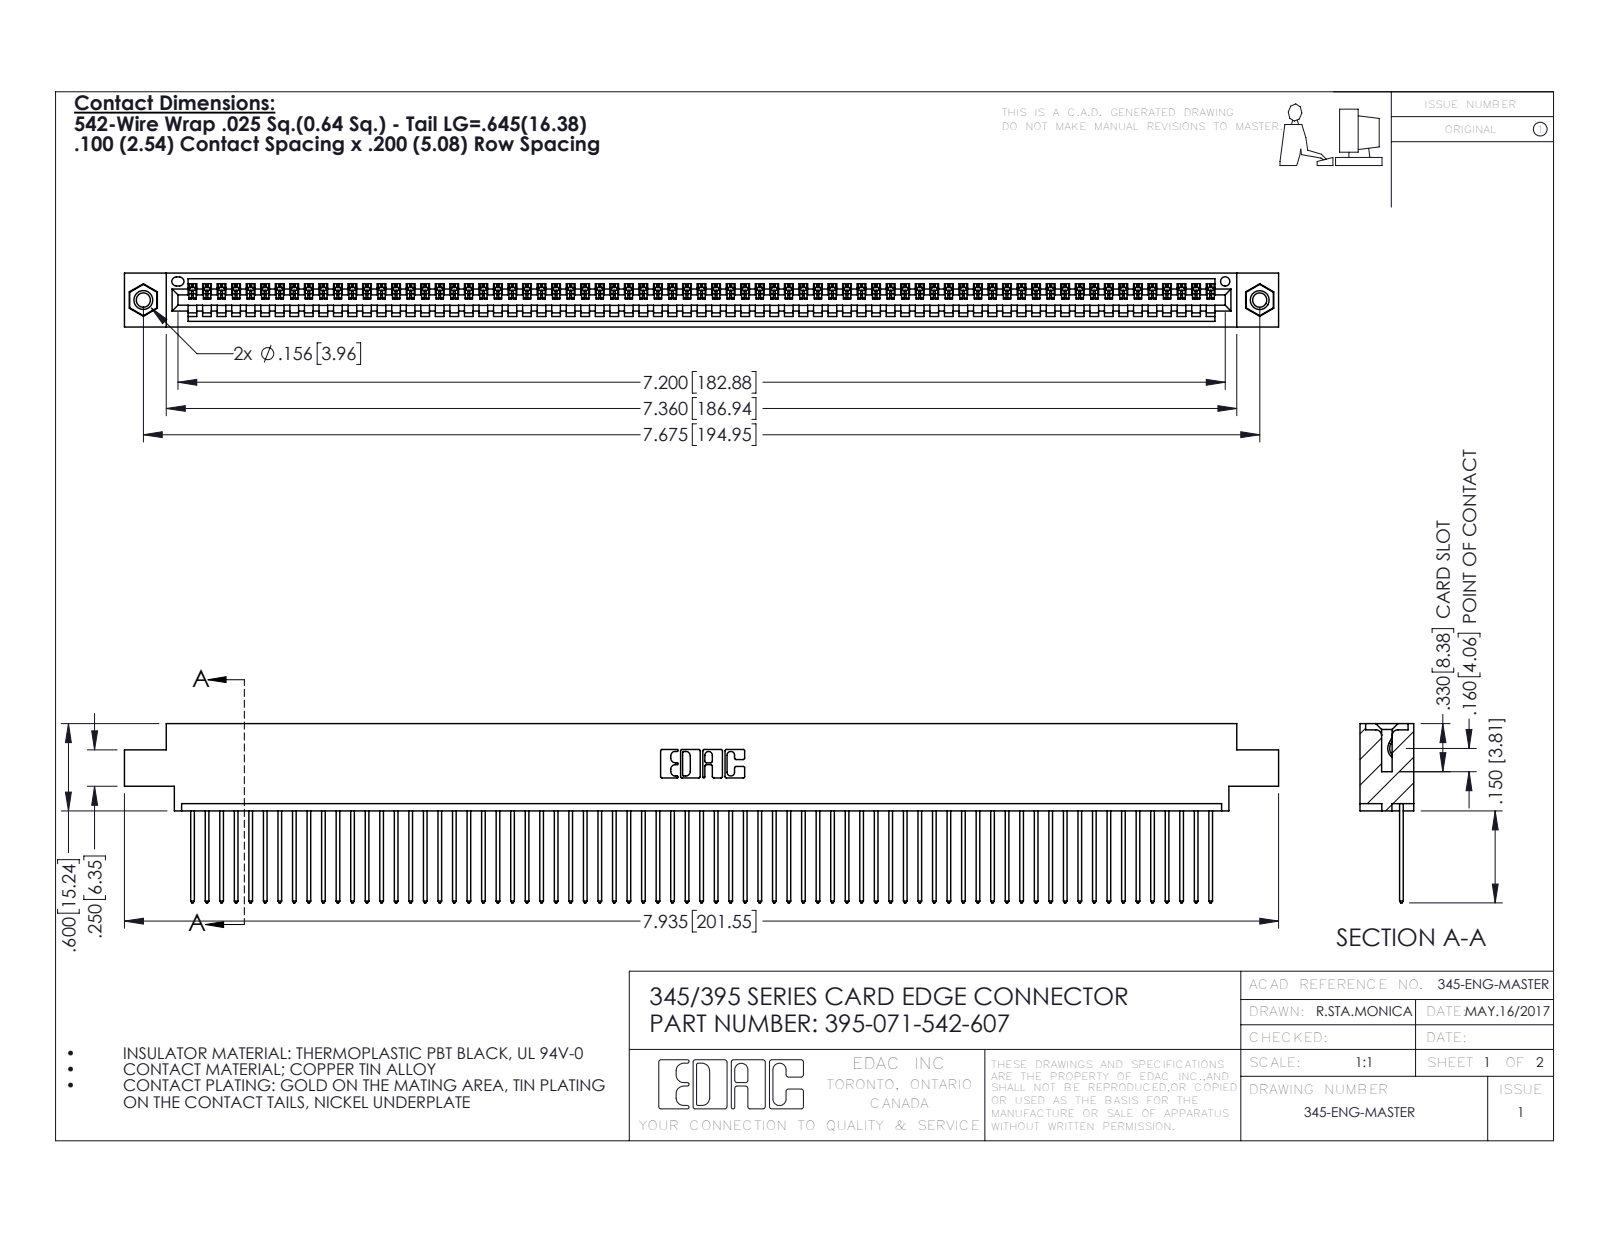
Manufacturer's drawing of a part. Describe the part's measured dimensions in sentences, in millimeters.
The part is named "345 Part_0.170 Offset - 0.156 Dia-TI; 345-250-001_345-250-005-103; 395-071-542-607; 345-292-001_345-293-142". Its 3-D file was written by "SolidWorks 2016 (CONFIG_CONTROL_DESIGN)". It is 74 solids with 4308 faces: 2956 planar, 1336 cylindrical and 16 other. Overall it measures 201.5 by 31.3 by 9.4 millimeters. Its volume is 19 420 cubic millimeters and its surface area 27 350 square millimeters. Round holes: 2 of diameter 2.5, 2 of diameter 3.2, 2 of diameter 4, 1 of diameter 1.6. Round bosses or shafts: 2 of diameter 3.9. Partial cylindrical surfaces (rounded edges, fillets, slot ends): 142 of radius 0.2, 142 of radius 0.3, 22 of radius 0.3, 6 of radius 0.2, 6 of radius 0.8, 3 of radius 0.7, 2 of radius 0.8, 2 of radius 1. The main face-to-face distances are 1.8, 7.6, 9.4, 2.5, 6.9, 0.6, 5.1, 5.7, 4.4, 3.8. The hole center spacings are 6.9, 189, 194.9.
